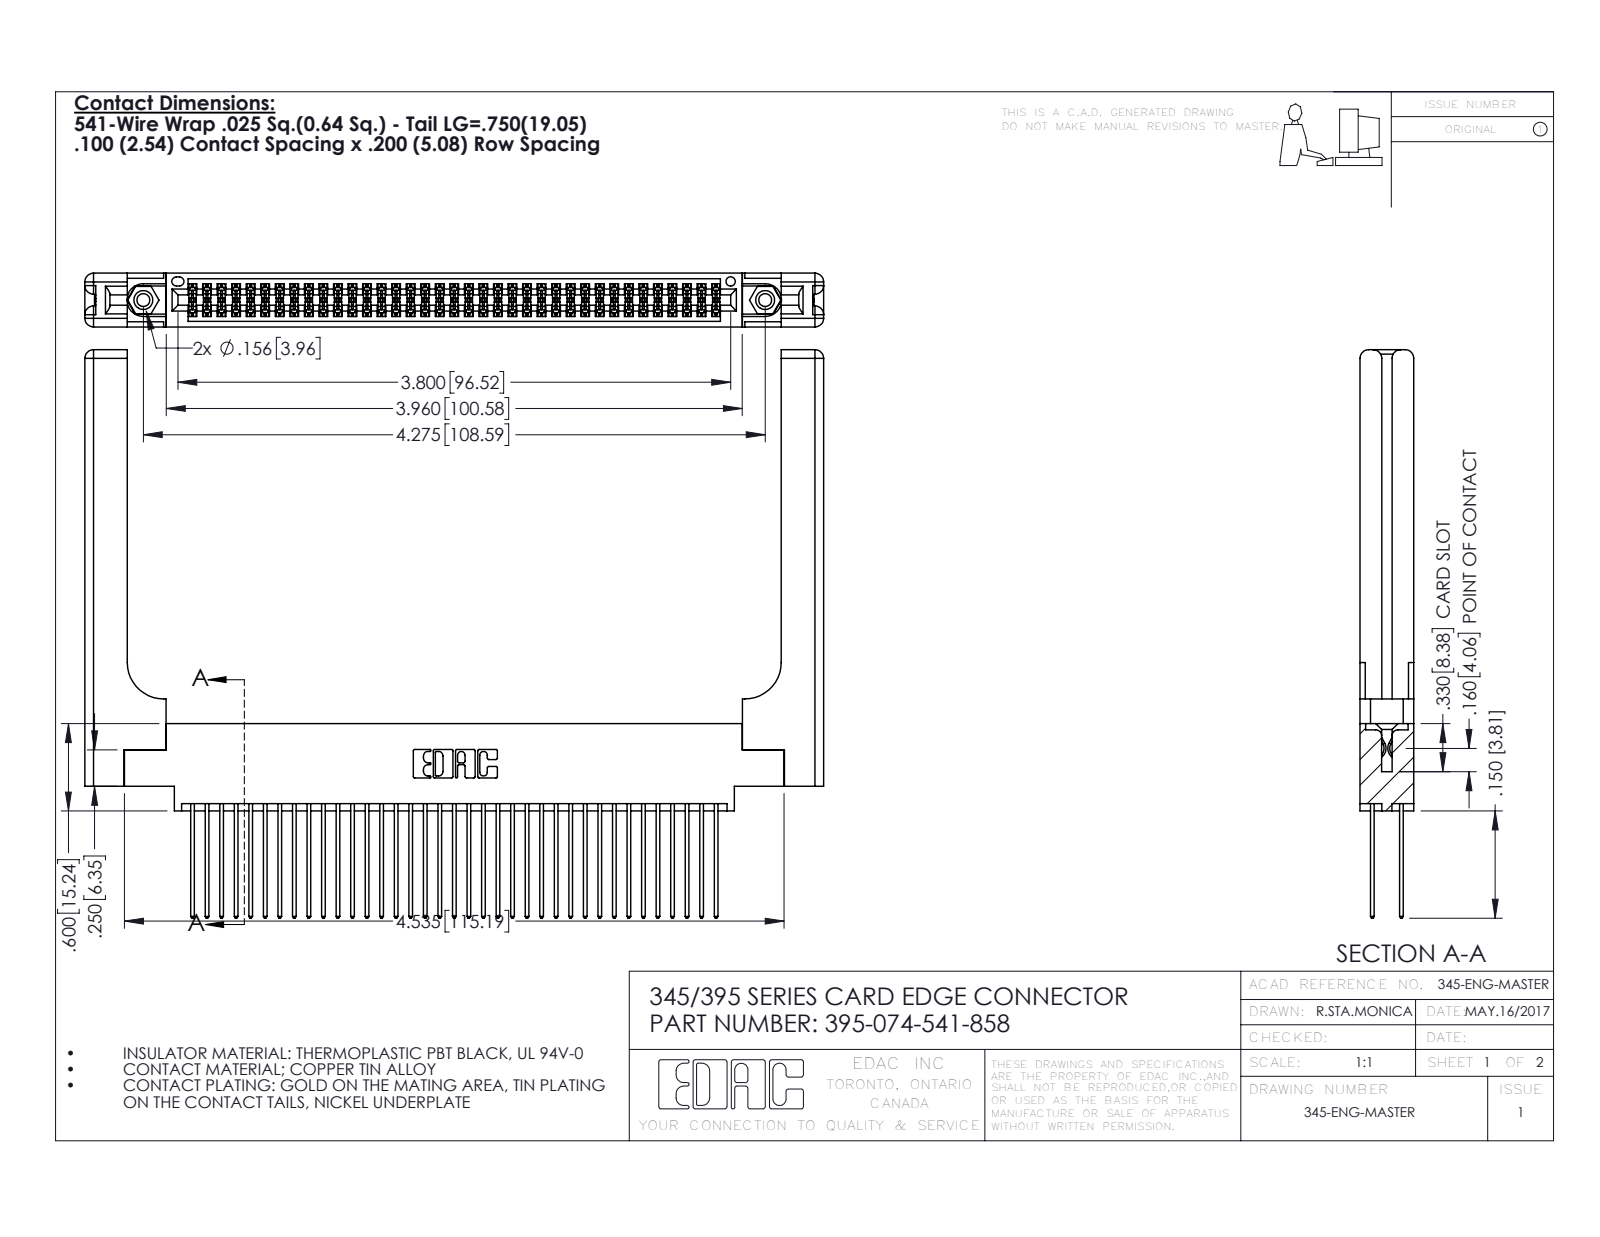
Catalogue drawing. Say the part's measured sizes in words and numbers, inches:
The part is named "345 Part_0.170 Offset - 0.156 Dia-TH; 345-220-058_345-220-058; 395-074-541-858; 345-292-001_345-293-141 (+1 more)". Its 3-D file was written by "SolidWorks 2016 (CONFIG_CONTROL_DESIGN)". It is 79 solids with 4086 faces: 2674 planar, 1352 cylindrical and 60 other. Overall it measures 5.079 by 3.907 by 0.37 inches. Its volume is 1.298 cubic inches and its surface area 40.33 square inches. Round holes: 2 of diameter 0.089, 2 of diameter 0.125, 2 of diameter 0.156, 1 of diameter 0.064. Round bosses or shafts: 2 of diameter 0.155. Partial cylindrical surfaces (rounded edges, fillets, slot ends): 111 of radius 0.006, 74 of radius 0.01, 22 of radius 0.01, 16 of radius 0.06, 6 of radius 0.007, 6 of radius 0.031, 3 of radius 0.026, 2 of radius 0.014. The main face-to-face distances are 0.072, 0.298, 0.37, 0.098, 0.272, 0.025, 0.2, 0.225, 0.175, 0.148. The hole center spacings are 0.27, 4.039, 4.275.
